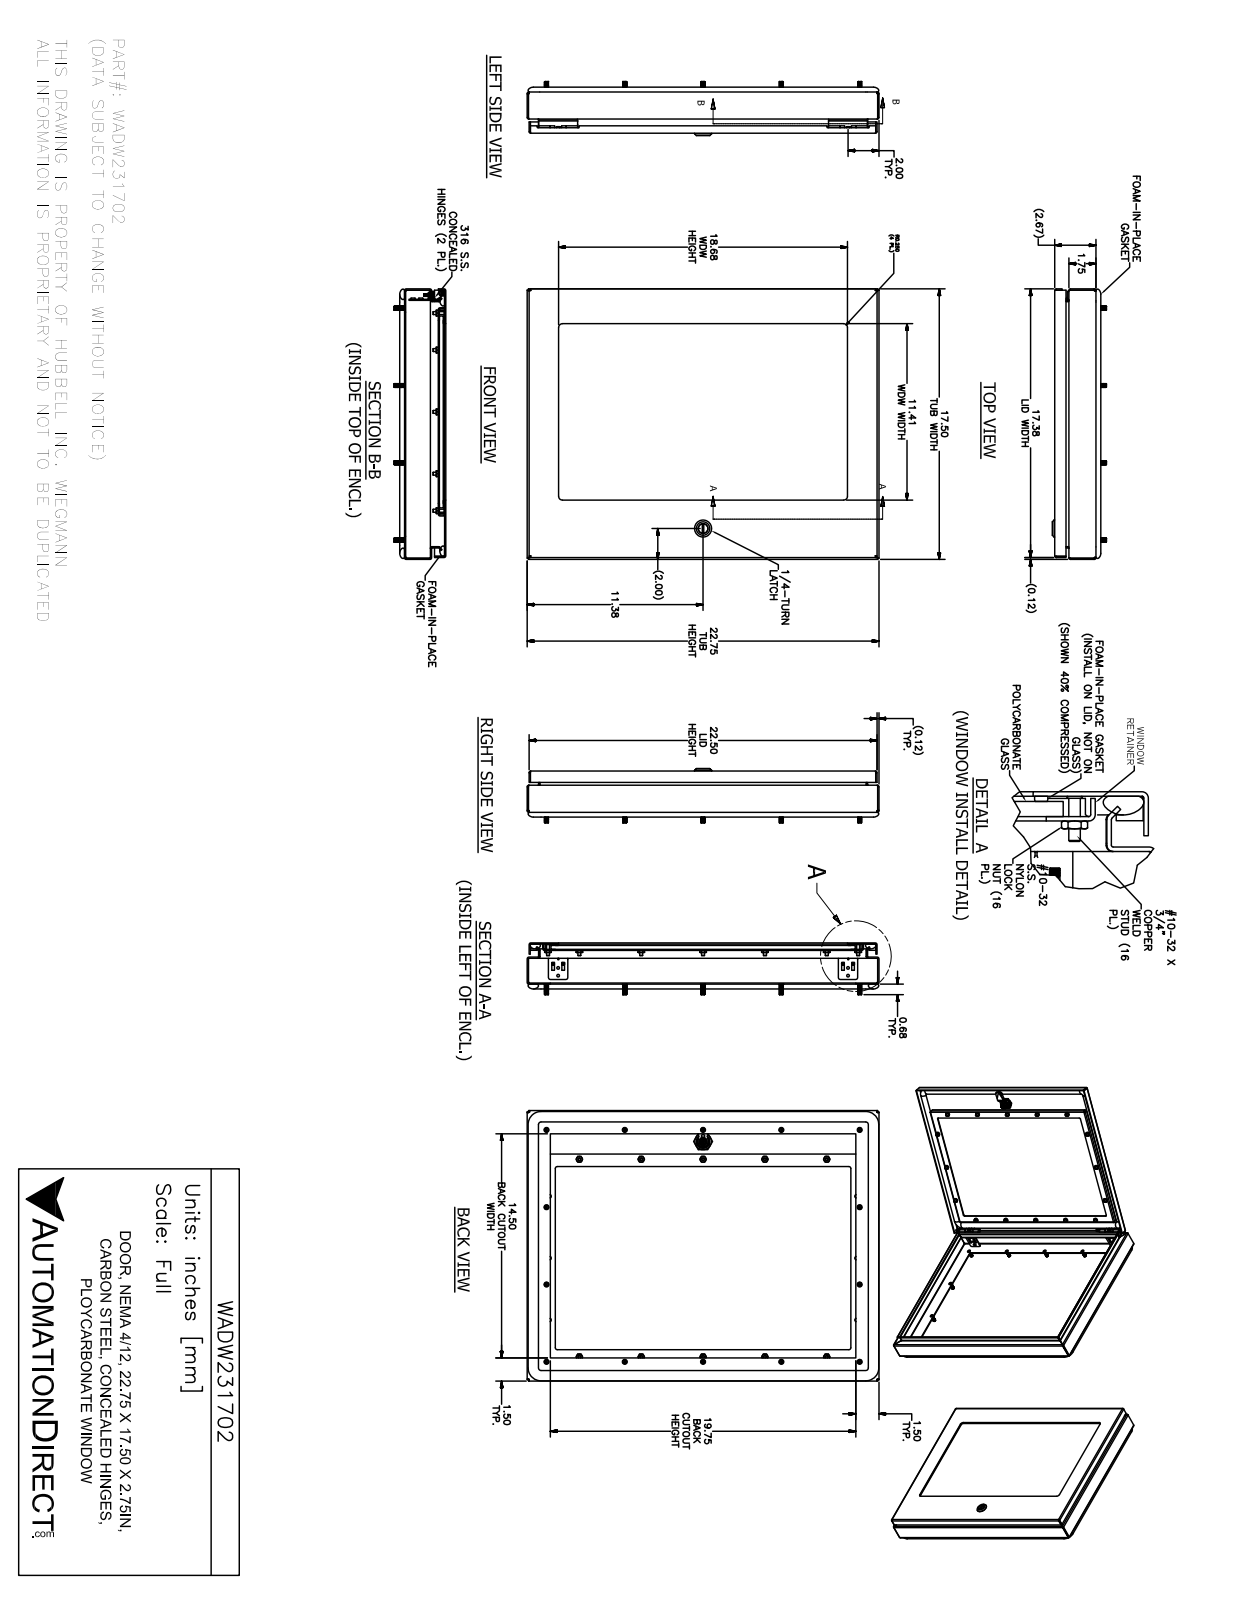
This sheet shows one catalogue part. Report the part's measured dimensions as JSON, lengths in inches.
{"part_name": "WADW231702", "step_written_by": "SolidWorks 2017 (AUTOMOTIVE_DESIGN)", "units": "inches", "bodies": {"solids": 76, "faces": 2095, "planar": 776, "cylindrical": 648, "other": 671}, "overall_size": [22.75, 17.5, 3.5], "volume_in3": 138.5, "surface_area_in2": 2115, "round_holes": [[0.156, 18], [0.281, 16], [0.249, 12], [0.093, 4], [0.152, 4], [0.167, 4], [0.172, 4], [0.188, 4], [0.187, 1], [0.197, 1], [0.315, 1], [0.394, 1]], "round_bosses_or_shafts": [[0.25, 24], [0.19, 16], [0.36, 4], [0.32, 4], [0.256, 4], [0.164, 4], [0.131, 4], [0.313, 2]], "partial_cylinders_radius": [[0.031, 34], [0.012, 30], [0.05, 26], [0.105, 24], [0.125, 20], [0.016, 18], [0.02, 13], [0.032, 8]], "face_to_face_distances": [0.074, 0.25, 0.337, 0.087, 0.411, 0.161, 2.593, 2.182, 2.432, 2.519], "hole_center_spacings": [4, 8, 13.396, 15.081, 12.785, 18.746, 6.706, 12]}
